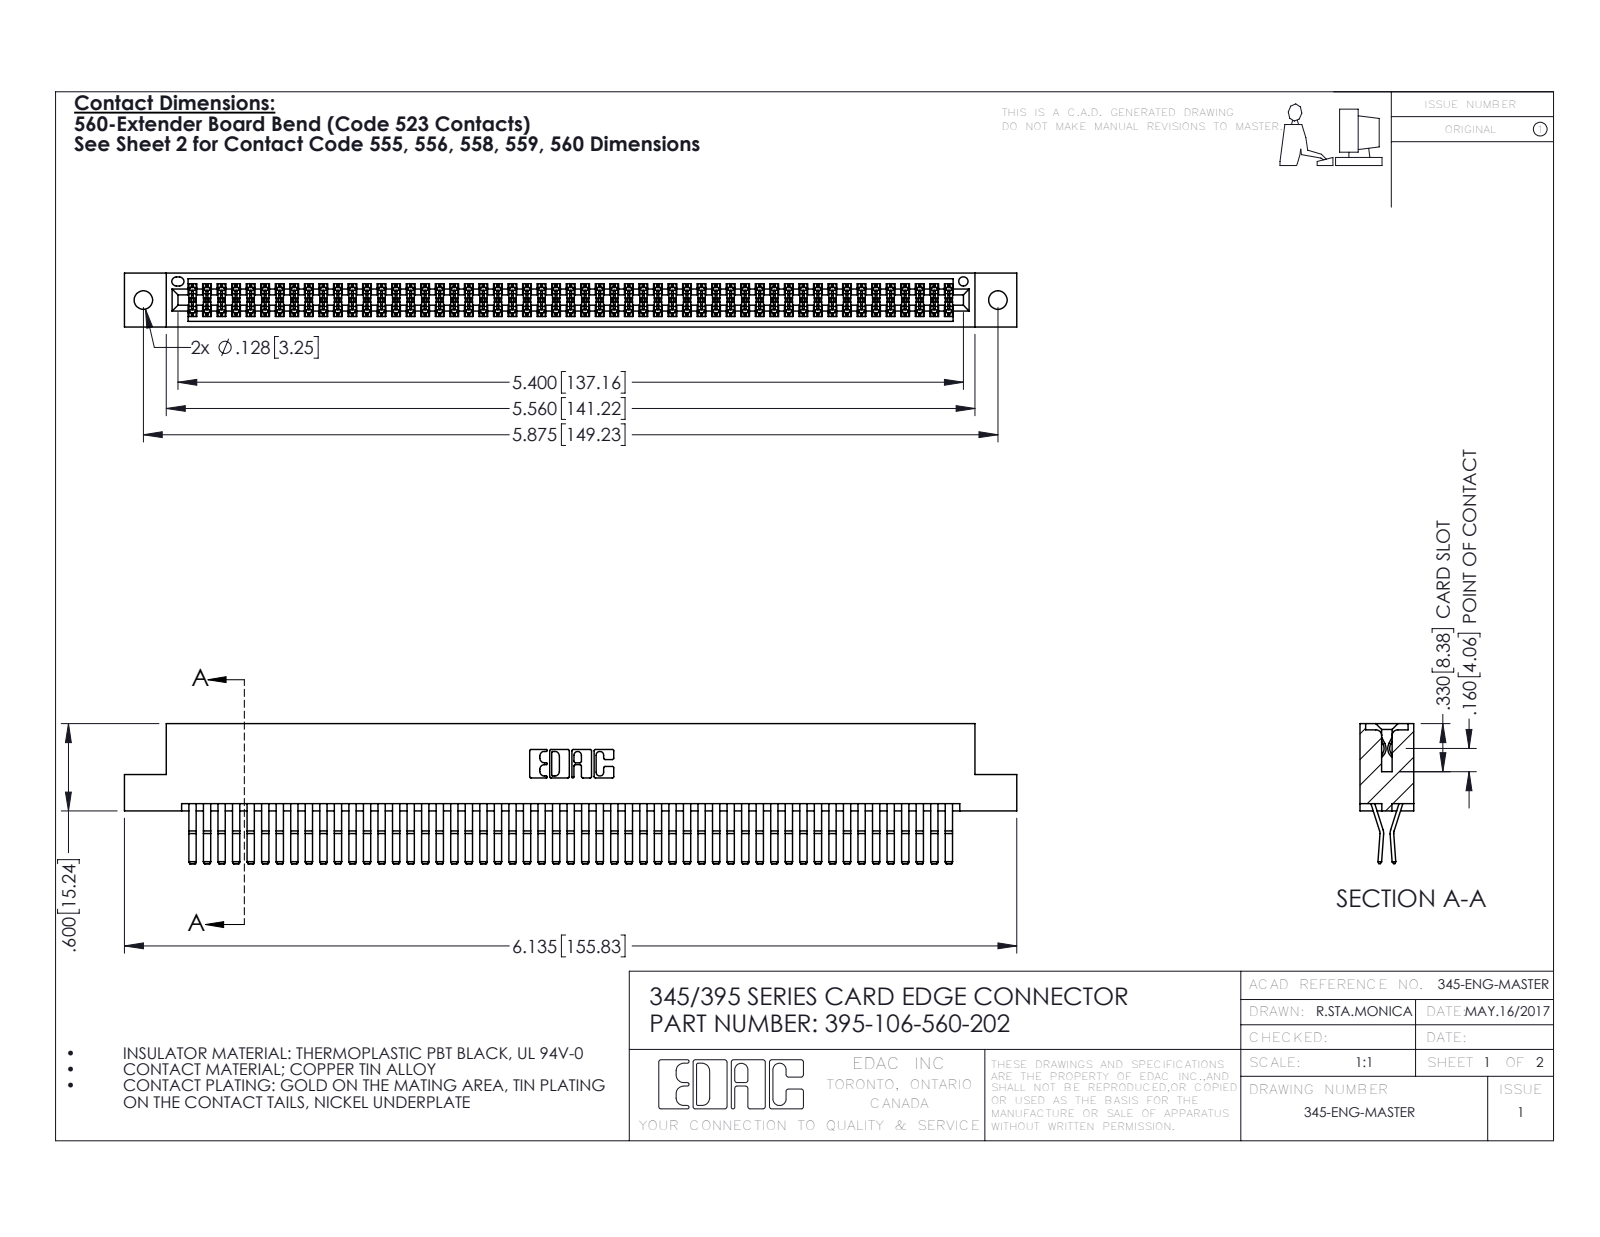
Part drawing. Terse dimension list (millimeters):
name: 345-292-001_560 Tail; 345 Part_Flush Mounting Lugs - 0.128 Dia; 395-106-560-202
written by: SolidWorks 2016 (CONFIG_CONTROL_DESIGN)
unit: mm
bodies: 107 solids, 5638 faces (3578 planar, 2060 cylindrical, 0 other)
size: 155.8 × 24.4 × 9.4
volume: 15 900 mm³; area: 25 230 mm²
holes: 2× ⌀3.3, 1× ⌀1.6
rounds: 159× R0.2, 22× R0.3, 6× R0.2, 6× R0.8, 3× R0.7, 2× R0.3, 2× R0.4, 2× R0.5
face distances: 0.6, 7.6, 1.8, 9.4, 5.1, 2.5, 6.9, 5.7, 4.4, 3.8
hole spacings: 6.9, 143.2, 149.2
